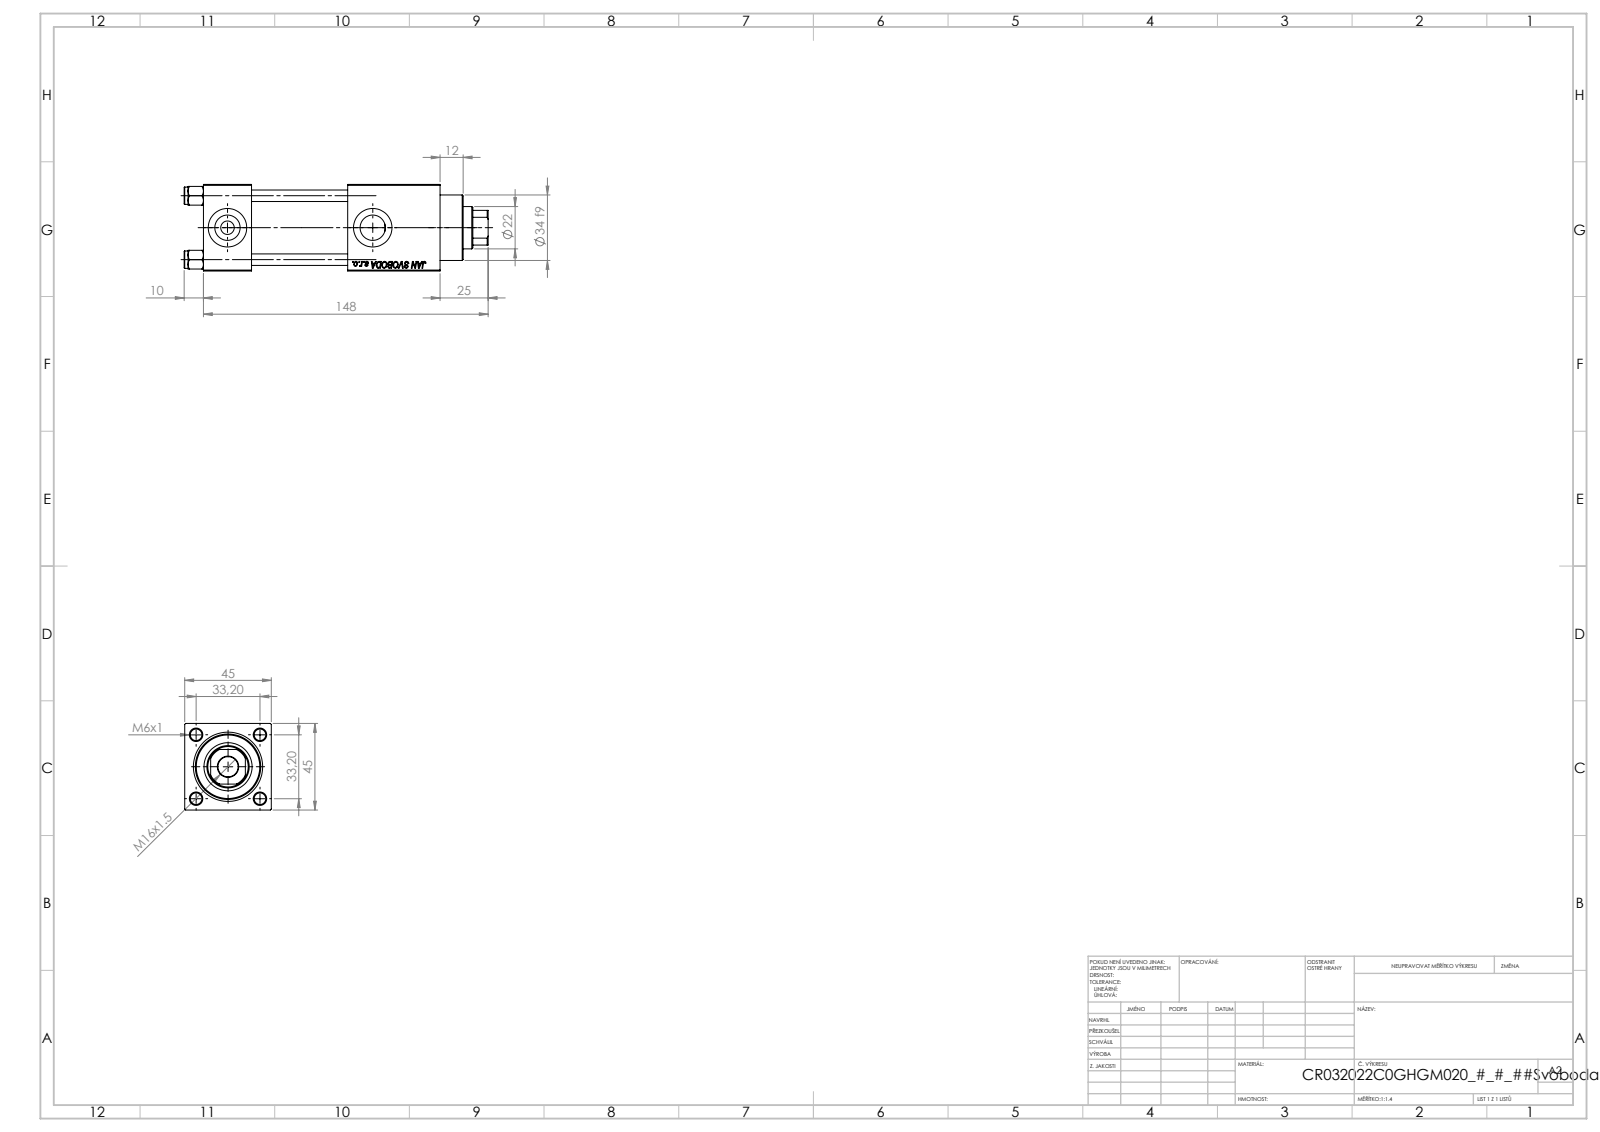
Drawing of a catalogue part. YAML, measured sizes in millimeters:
part_name: "NUT_M5_C; V215_VC_A; V215CR_C_Body; V215CR_C_TYCINKA (+1 more)"
step_written_by: "SolidWorks 2019 (CONFIG_CONTROL_DESIGN)"
units: millimeters
bodies: {solids: 11, faces: 1147, planar: 525, cylindrical: 86, other: 536}
overall_size: [158, 45, 45]
volume: 209859
surface_area: 71302
round_holes:
  - {diameter: 6, count: 4}
  - {diameter: 7, count: 2}
  - {diameter: 13.16, count: 2}
  - {diameter: 20, count: 2}
  - {diameter: 10.5, count: 1}
  - {diameter: 22, count: 1}
  - {diameter: 24, count: 1}
  - {diameter: 25, count: 1}
  - {diameter: 32, count: 1}
  - {diameter: 33, count: 1}
round_bosses_or_shafts:
  - {diameter: 9, count: 4}
  - {diameter: 38, count: 1}
  - {diameter: 34, count: 1}
partial_cylinders:
  - {radius: 10.5, count: 1}
face_to_face_distances: [45, 25, 50, 123, 75, 98, 48, 94.3, 69.3, 19.3]
hole_center_spacings: [23.48, 33.2, 46.95, 75.5]
